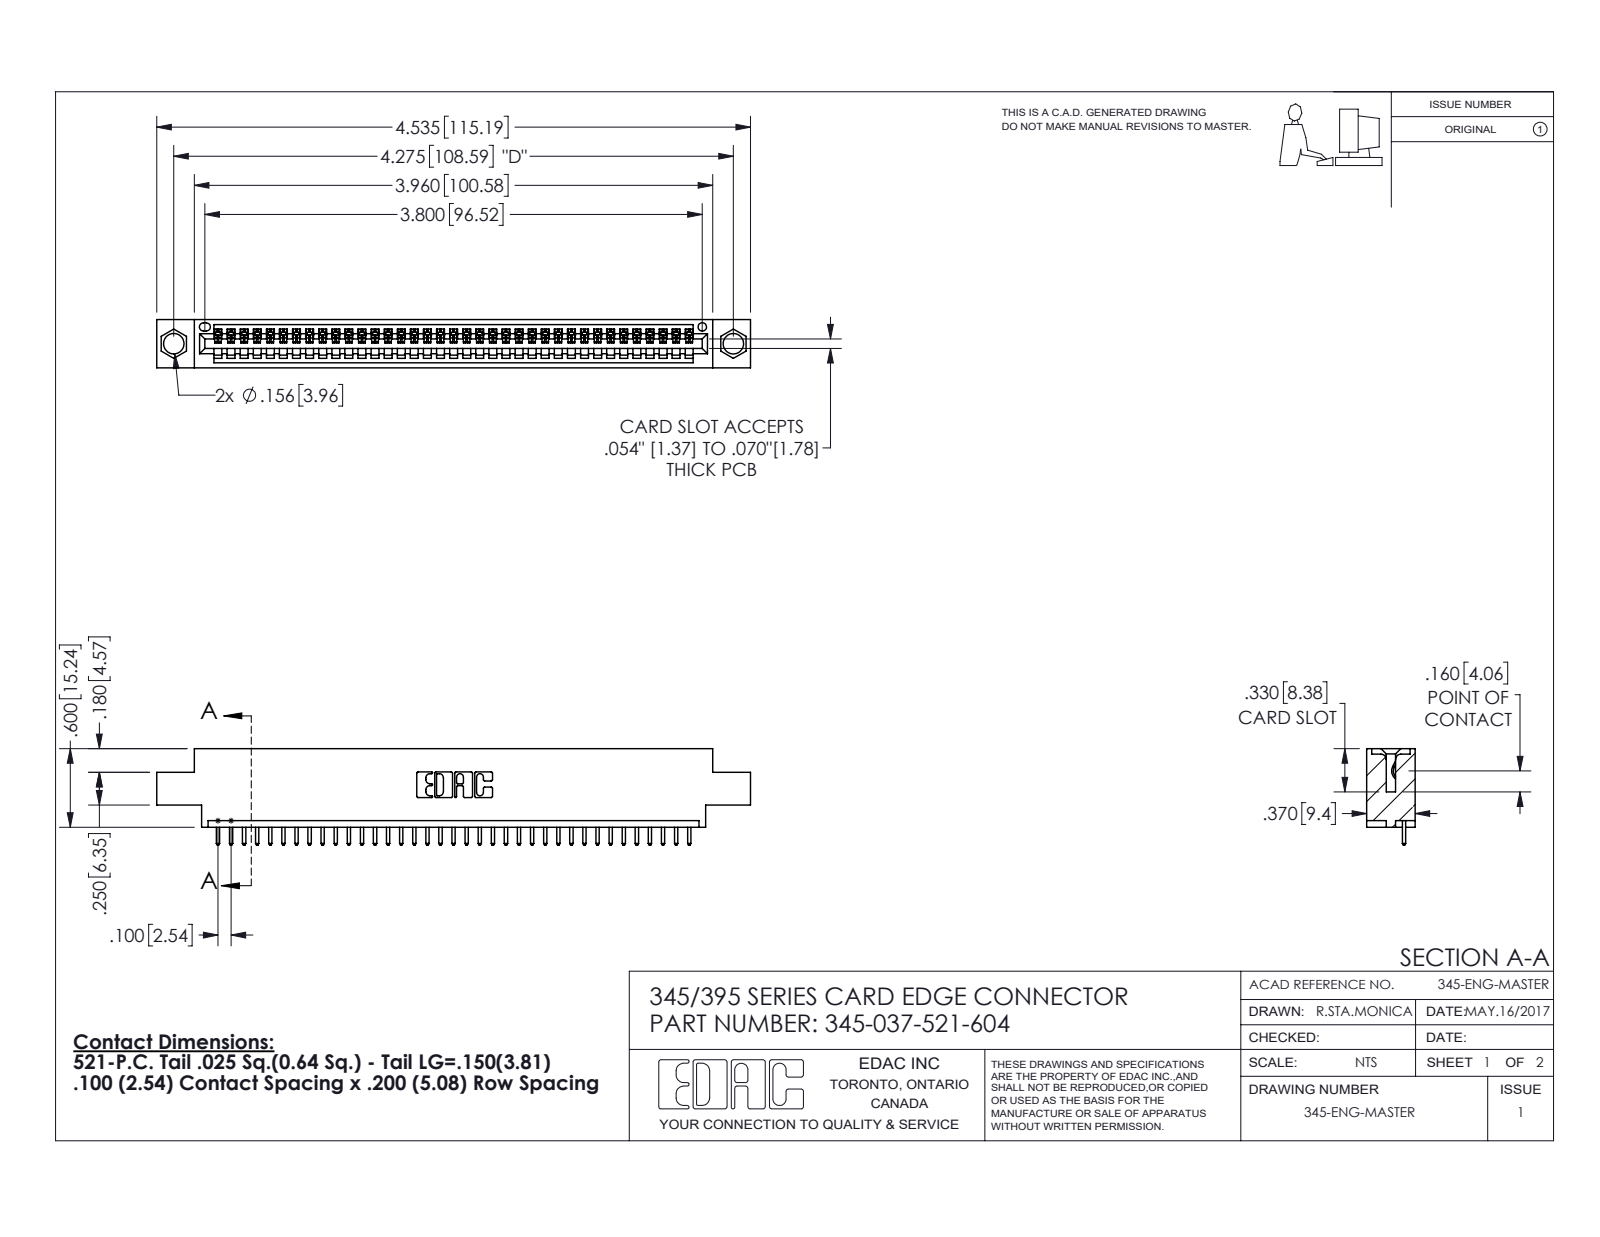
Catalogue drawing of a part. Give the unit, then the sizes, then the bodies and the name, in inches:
Units: inches
Overall size (bounding box): 4.535 × 0.737 × 0.37
Round holes (diameter × count): ⌀0.156 ×2, ⌀0.064 ×1
Partial cylindrical surfaces — rounded edges, fillets, slot ends (radius × count): R0.006 ×74, R0.01 ×74, R0.01 ×22, R0.007 ×6, R0.031 ×6, R0.026 ×3, R0.031 ×2, R0.04 ×2
Main face-to-face distances: 0.298, 0.072, 0.37, 0.2, 0.098, 0.272, 0.025, 0.225, 0.175, 0.149
Hole centre spacings: 0.27, 4.039, 4.275
Volume: 0.646 in³ · Surface area: 20.98 in²
Bodies: 38 solids, 2276 faces (1564 planar, 712 cylindrical, 0 other)
Part name (STEP PRODUCT): 345 Part_0.170 Offset - 0.156 Dia-TH; 345-037-521-604; 345-292-001_345-293-121
STEP written by: SolidWorks 2016 (CONFIG_CONTROL_DESIGN)
